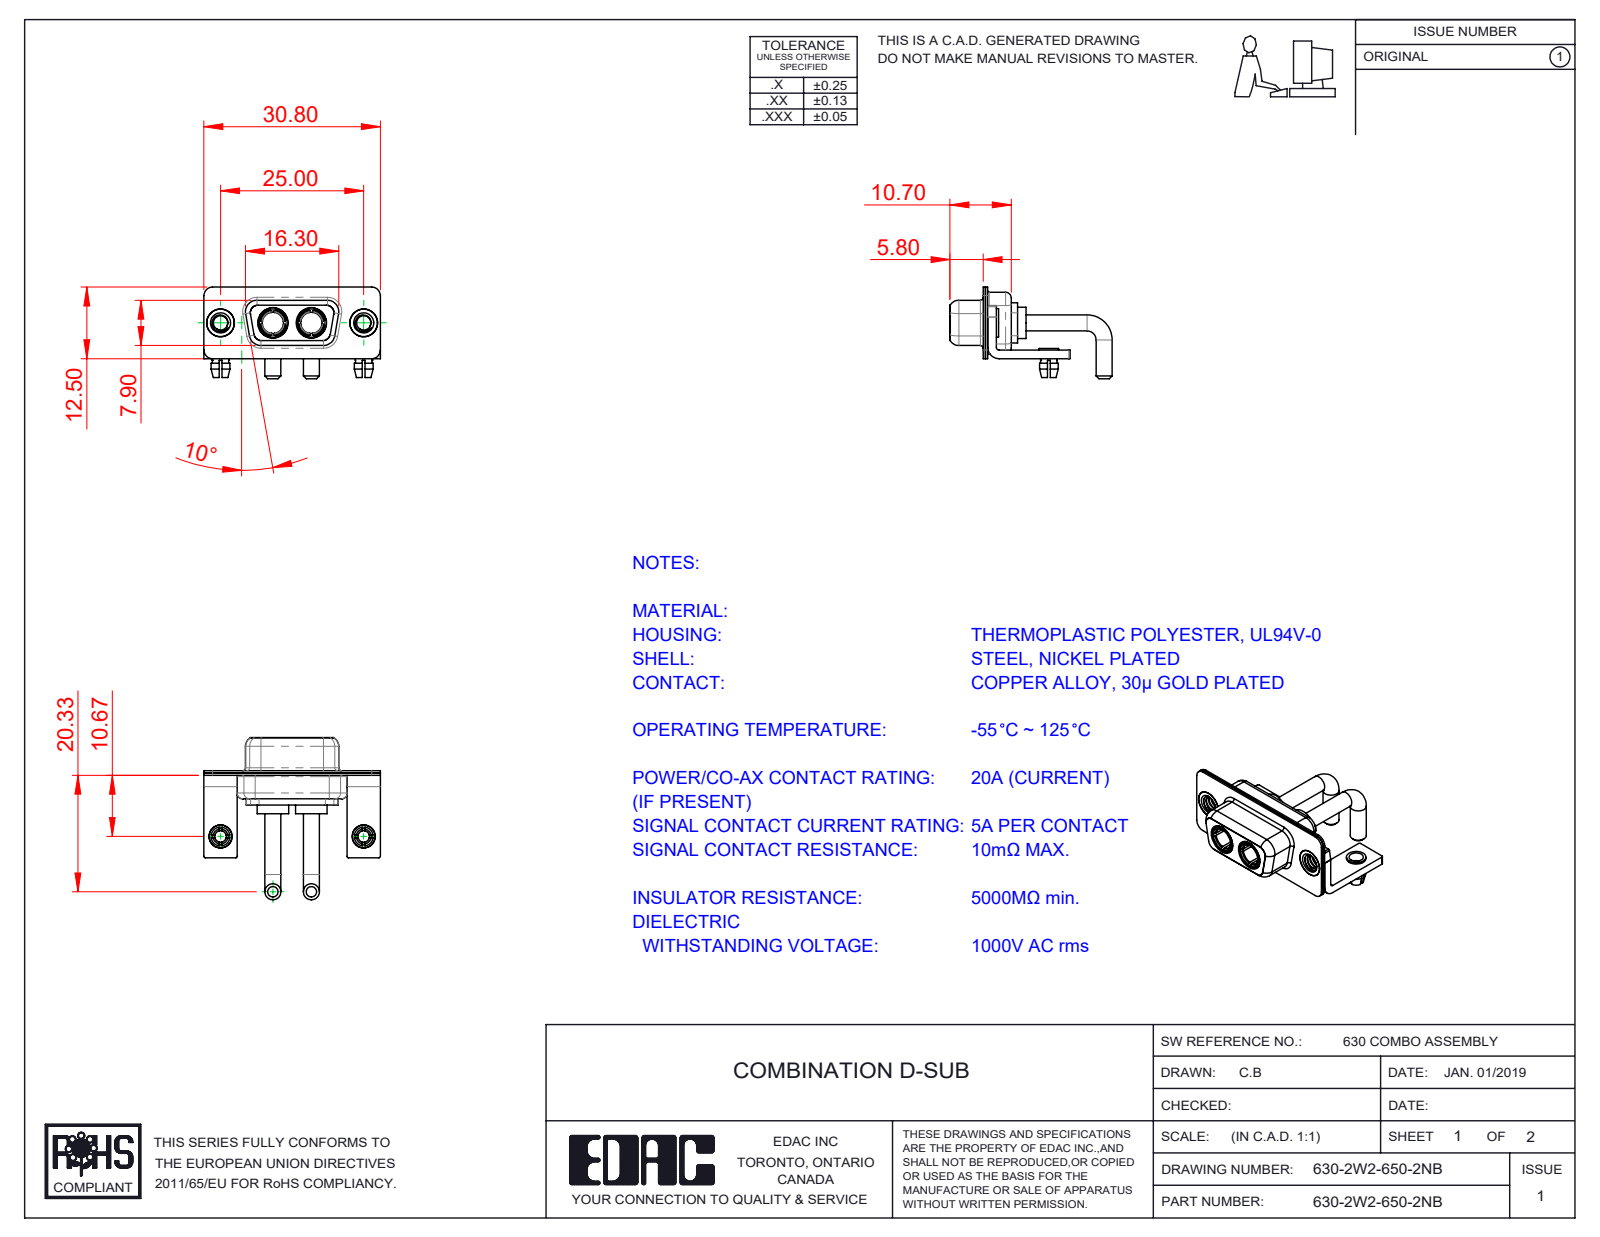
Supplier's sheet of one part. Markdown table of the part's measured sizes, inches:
| quantity | value |
| --- | --- |
| part name | 630Combo Shell Rear_09 Contacts; 630Combo Shell Front_09 Contacts; 630Combo Threaded Rivet_B; 630Combo Housing_2W2 (+4 more) |
| STEP written by | SolidWorks 2020 (CONFIG_CONTROL_DESIGN) |
| units | inches |
| bodies | 13 solids, 565 faces (193 planar, 237 cylindrical, 135 other) |
| overall size | 1.213 × 1.115 × 0.63 |
| volume | 0.134 in³ |
| surface area | 8.241 in² |
| round holes (diameter × count) | 0.098 × 4, 0.191 × 4, 0.079 × 2, 0.126 × 2, 0.146 × 2, 0.157 × 2, 0.159 × 2, 0.209 × 2 |
| round bosses / shafts (diameter × count) | 0.11 × 4, 0.217 × 2, 0.205 × 2, 0.197 × 2, 0.195 × 2, 0.195 × 2, 0.189 × 2, 0.187 × 2 |
| partial cylindrical surfaces (radius × count) | 0.01 × 16, 0.059 × 16, 0.079 × 13, 0.053 × 8, 0.063 × 8, 0.02 × 5, 0.024 × 4, 0.026 × 4 |
| main face-to-face distances | 0.016, 0.059, 0.031, 0.055, 0.018, 0.333, 0.071, 0.091, 0.35, 0.146 |
| hole center spacings | 0.36, 0.624, 0.984, 0.265 |
